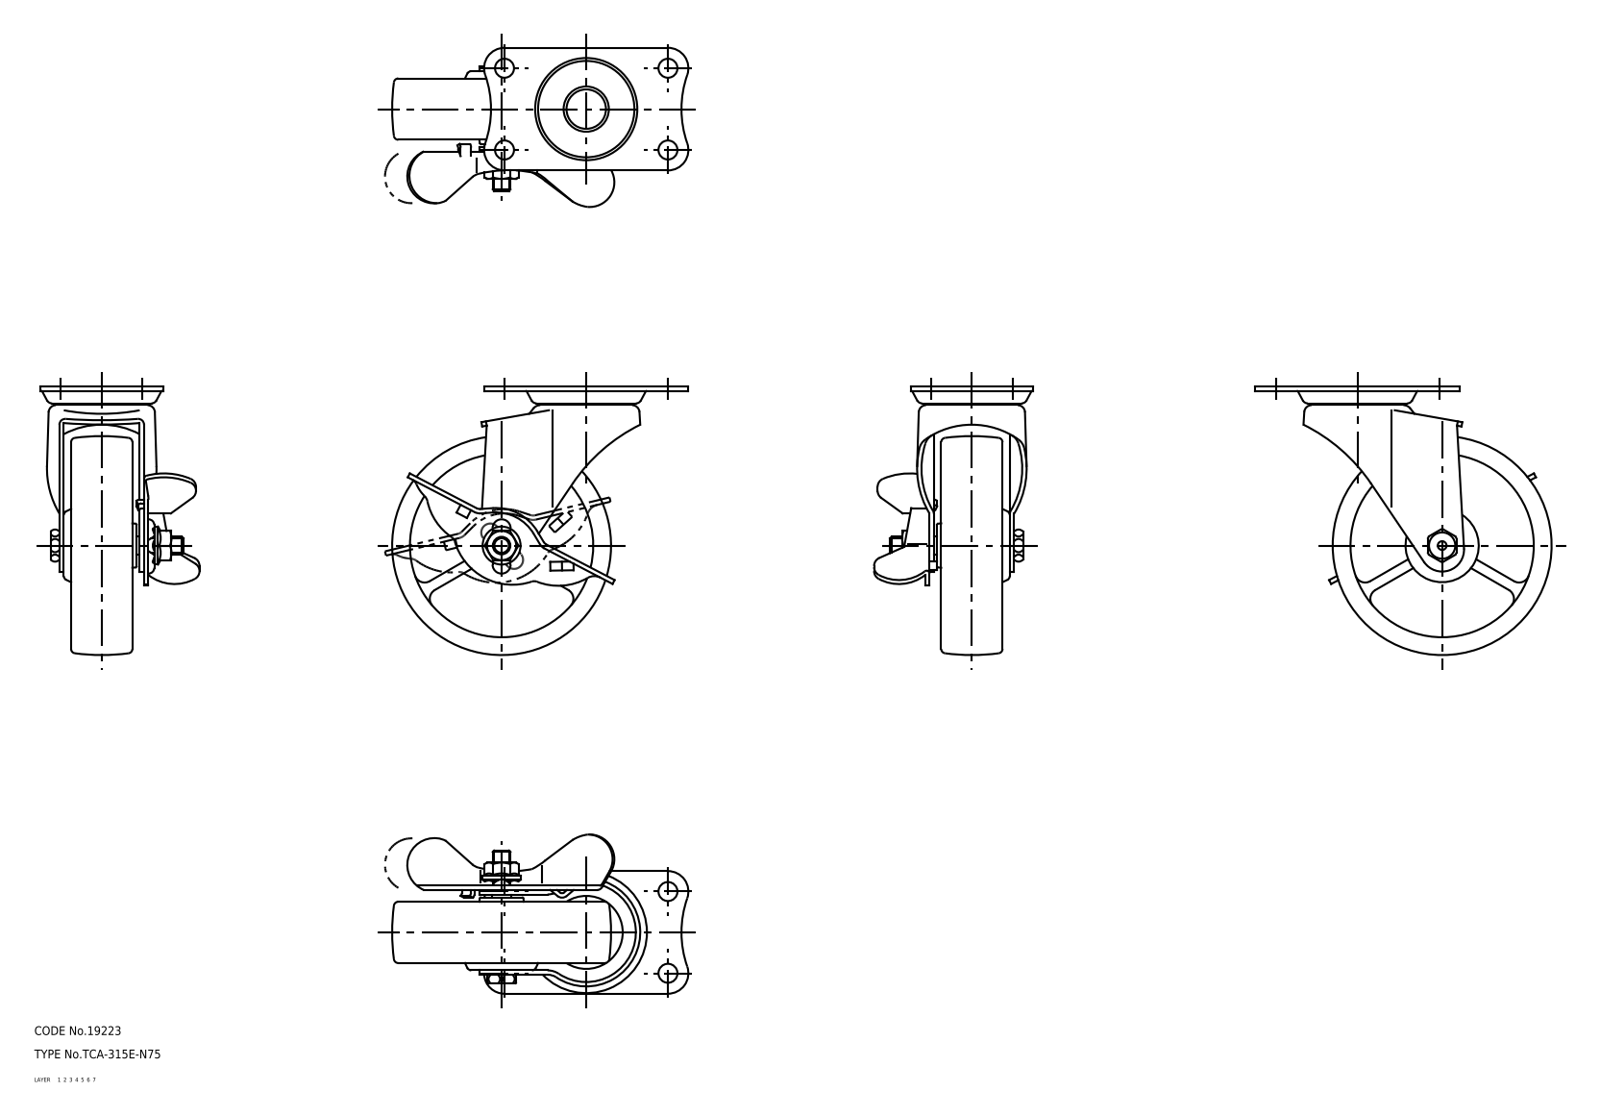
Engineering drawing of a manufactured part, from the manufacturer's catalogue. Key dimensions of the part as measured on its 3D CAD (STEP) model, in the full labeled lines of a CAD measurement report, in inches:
Part name (STEP PRODUCT): lever; wheel; mounting plate; main shaft (+2 more)
STEP written by: CADfix (AUTOMOTIVE_DESIGN)
Units: inches
Bodies: 8 solids, 569 faces (0 planar, 0 cylindrical, 569 other)
Overall size (bounding box): 3.996 × 3.622 × 2.14
Volume: 5.185 in³ · Surface area: 65.68 in²
